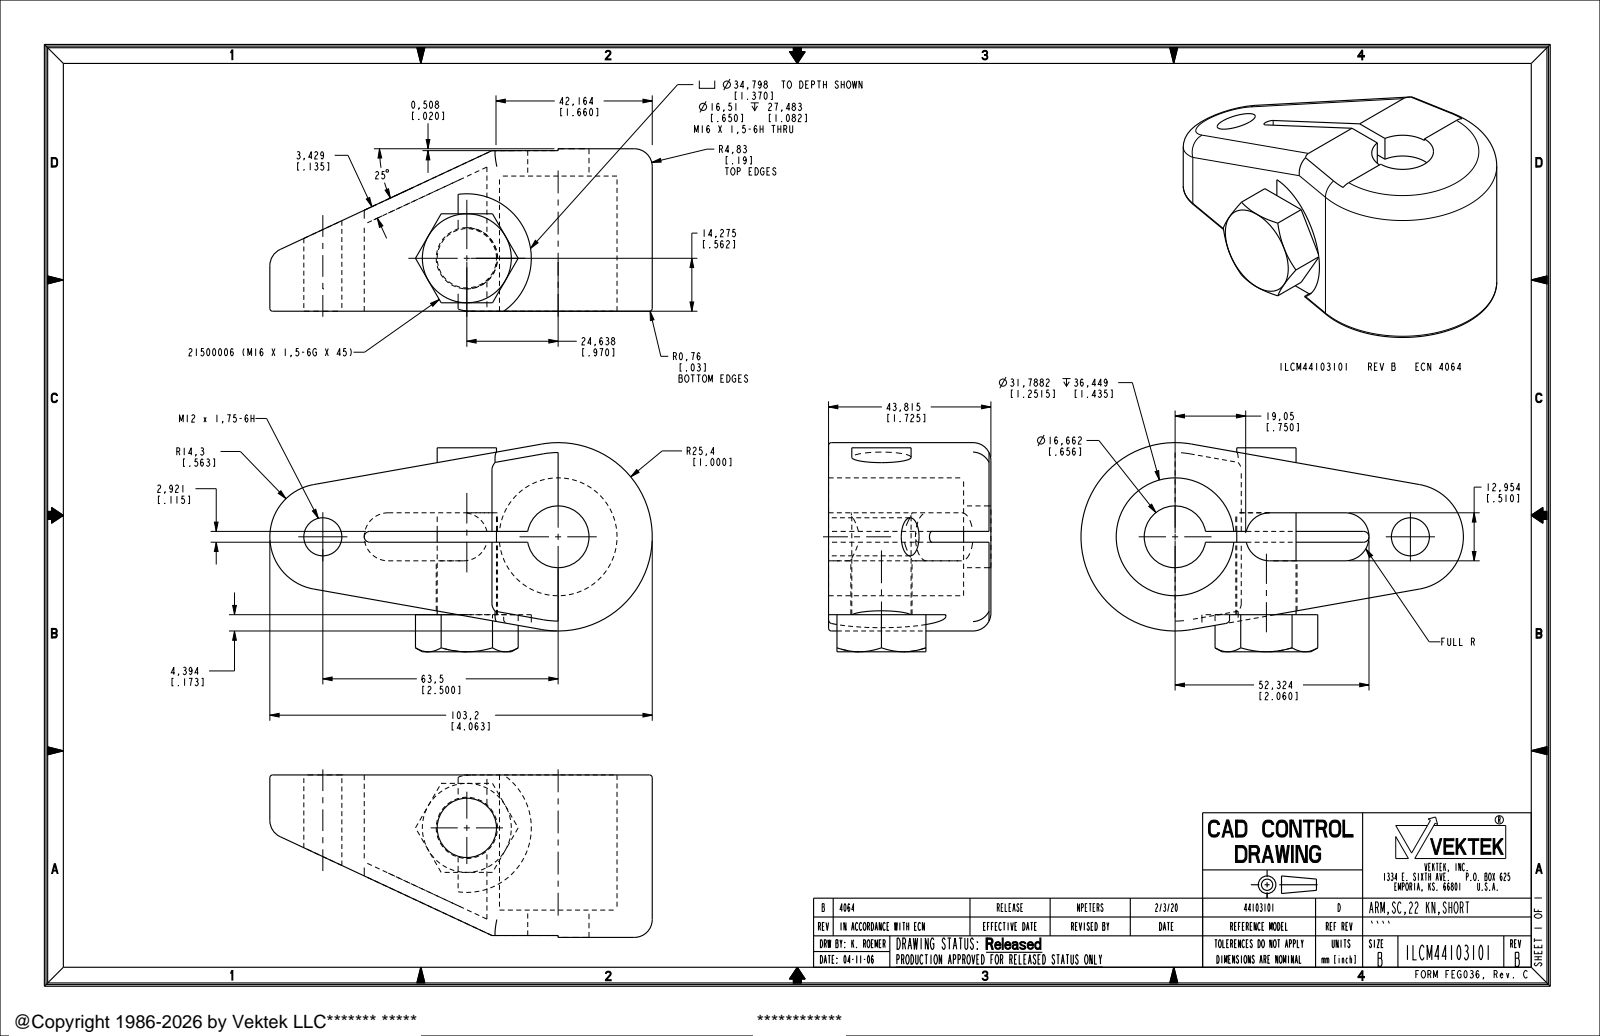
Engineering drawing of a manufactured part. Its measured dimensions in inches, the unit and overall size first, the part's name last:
Units: inches
Overall size (bounding box): 4.063 × 2.221 × 1.725
Round holes (diameter × count): ⌀0.404 ×1, ⌀0.65 ×1, ⌀0.656 ×1, ⌀1.252 ×1
Round bosses / shafts (diameter × count): ⌀0.63 ×1
Partial cylindrical surfaces — rounded edges, fillets, slot ends (radius × count): R0.19 ×4, R0.03 ×2, R0.255 ×2, R0.057 ×1, R0.563 ×1, R0.685 ×1, R1 ×1
Main face-to-face distances: 1.705, 0.198, 0.313, 1.725, 0.02, 1.435, 0.27, 0.29, 0.51, 0.966
Hole centre spacings: 2.5
Volume: 6.389 in³ · Surface area: 40.76 in²
Bodies: 1 solid, 63 faces (26 planar, 27 cylindrical, 10 other)
Part name (STEP PRODUCT): ILCM44103101
STEP written by: PRO/ENGINEER BY PARAMETRIC TECHNOLOGY CORPORATION, 2013320 (AUTOMOTIVE_DESIGN)
